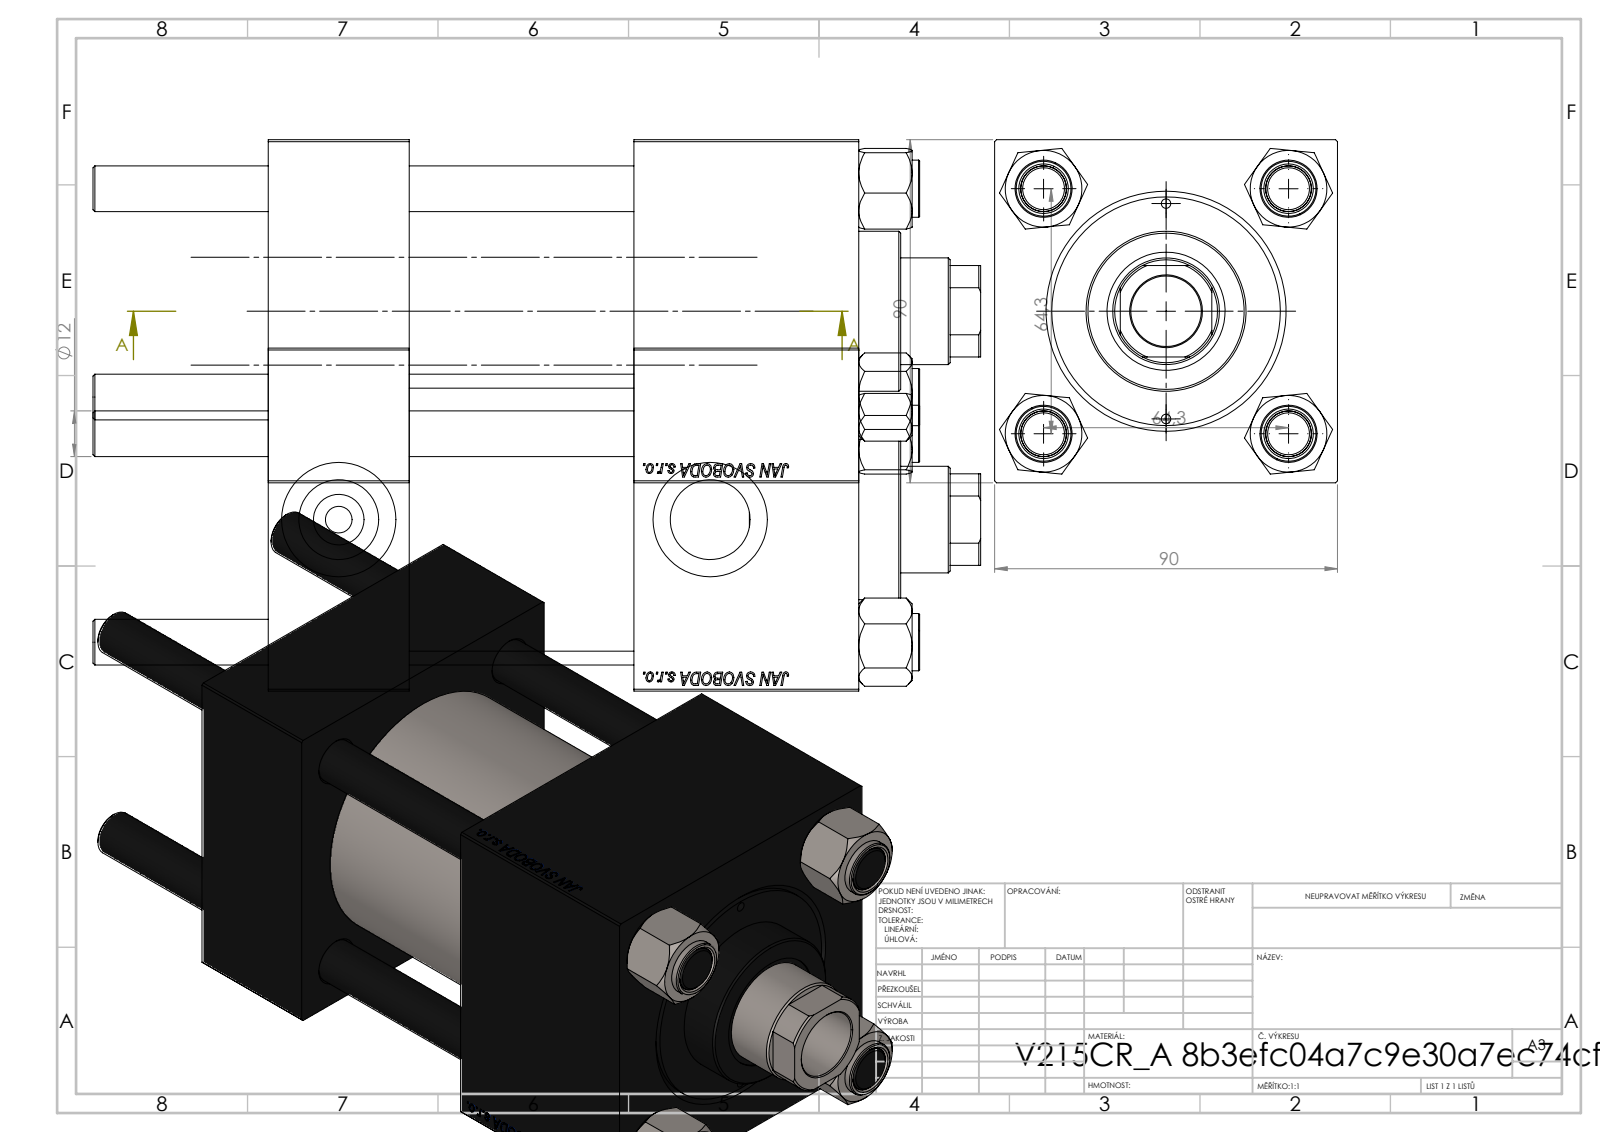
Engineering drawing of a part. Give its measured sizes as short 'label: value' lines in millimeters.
name: V215CR_VCP; V215CR_BODY_A; NUT_M5; V215_VC_A (+1 more)
written by: SolidWorks 2019 (CONFIG_CONTROL_DESIGN)
unit: mm
bodies: 11 solids, 1140 faces (522 planar, 82 cylindrical, 536 other)
size: 233 × 90 × 90
volume: 981 237 mm³; area: 195 342 mm²
holes: 4× ⌀12, 2× ⌀2.5, 2× ⌀7, 2× ⌀20.96, 2× ⌀30, 1× ⌀18.5, 1× ⌀28, 1× ⌀31, 1× ⌀50, 1× ⌀60, 1× ⌀63
bosses: 4× ⌀15, 1× ⌀69, 1× ⌀42
rounds: 1× R13.5
face distances: 90, 59, 37, 155, 118, 96, 126.3, 89.3, 30.3, 28.7
hole spacings: 32.39, 45.47, 64.3, 68.42, 28.25, 90.93, 56.5, 97.5
